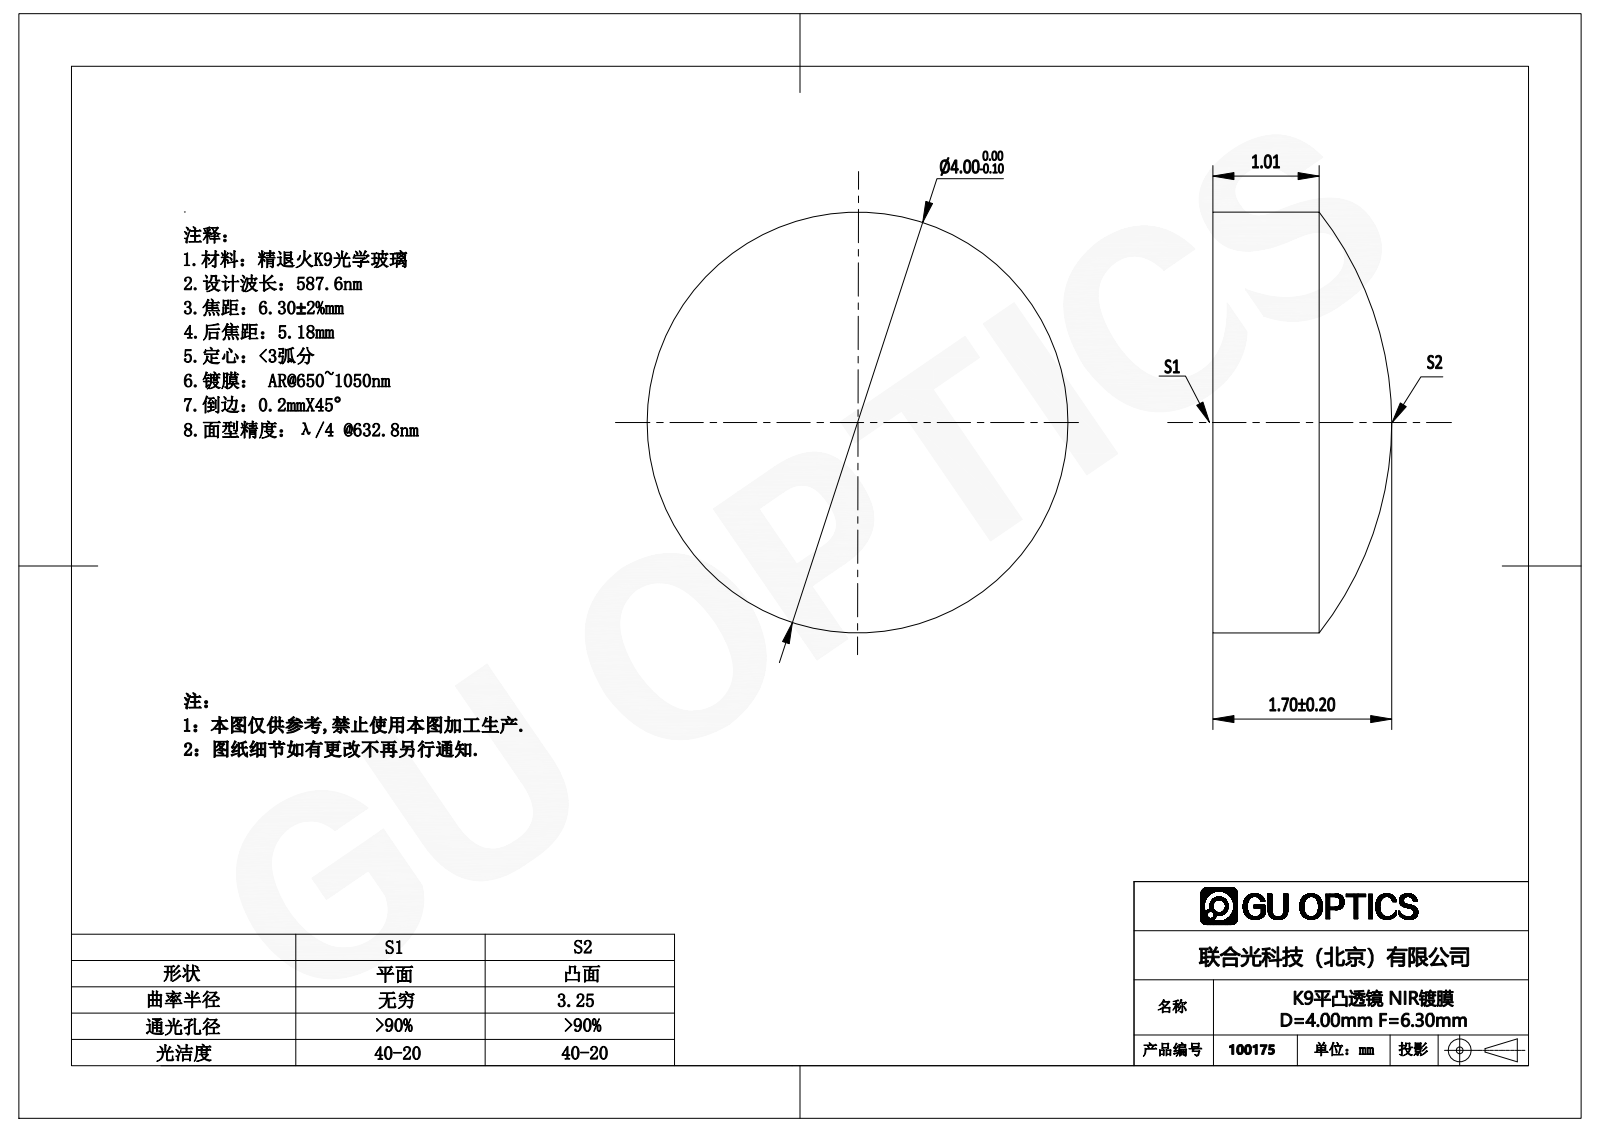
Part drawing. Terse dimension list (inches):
name: 100175
written by: SolidWorks 2016 (AUTOMOTIVE_DESIGN)
unit: in
bodies: 1 solid, 5 faces (1 planar, 2 cylindrical, 2 other)
size: 0.157 × 0.157 × 0.067
volume: 0.001 in³; area: 0.06 in²
bosses: 1× ⌀0.157
